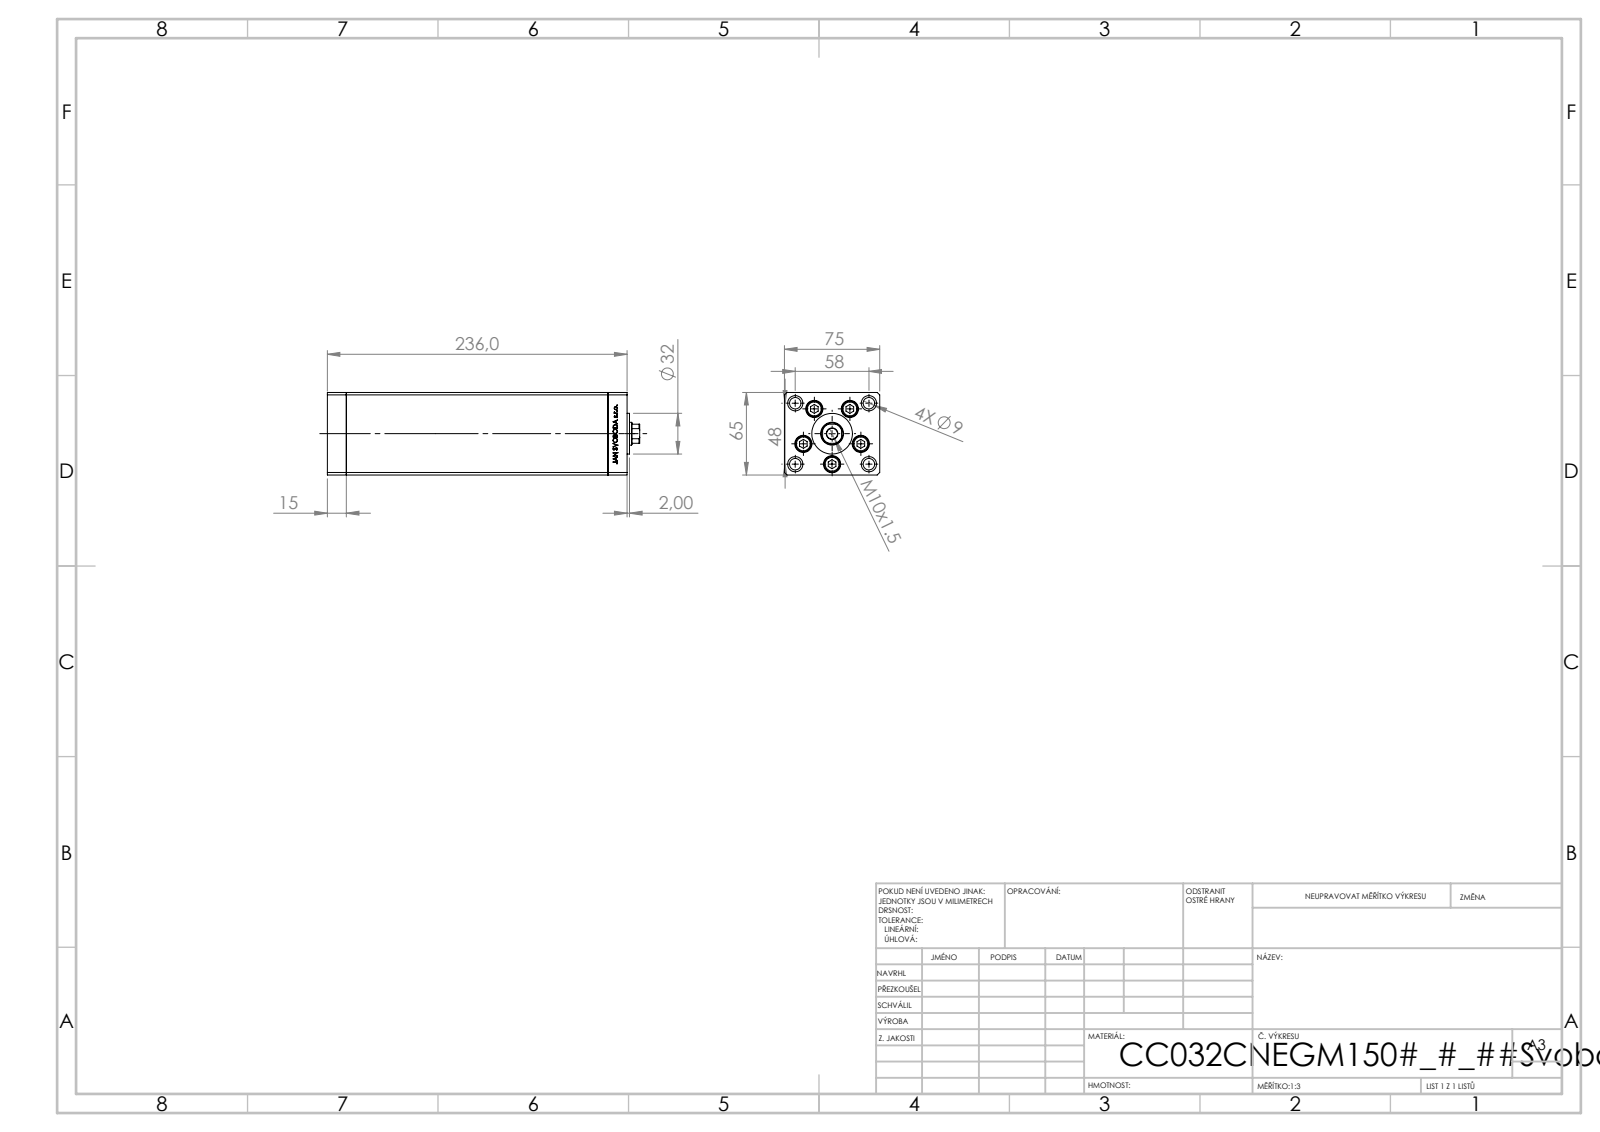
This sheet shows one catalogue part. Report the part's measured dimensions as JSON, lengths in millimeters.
{"part_name": "V220C FRONT; V220C_VC_C; ALLEN BOLT; V220C_C MIDDLE (+1 more)", "step_written_by": "SolidWorks 2019 (CONFIG_CONTROL_DESIGN)", "units": "millimeters", "bodies": {"solids": 13, "faces": 1163, "planar": 542, "cylindrical": 159, "other": 462}, "overall_size": [246, 75, 65], "volume_mm3": 965657, "surface_area_mm2": 176965, "round_holes": [[9, 9], [13.5, 5], [8, 4], [12, 4], [8.5, 1], [12.5, 1], [18, 1]], "round_bosses_or_shafts": [[8, 5], [12.5, 4], [32, 1]], "partial_cylinders_radius": [[0.93, 2], [8.5, 1]], "face_to_face_distances": [75, 65, 15, 206, 221, 236, 54.5, 10.5, 26.25, 48.75], "hole_center_spacings": [24, 37.64, 15.67, 17.22, 27.71, 28.83, 29, 32.63]}
